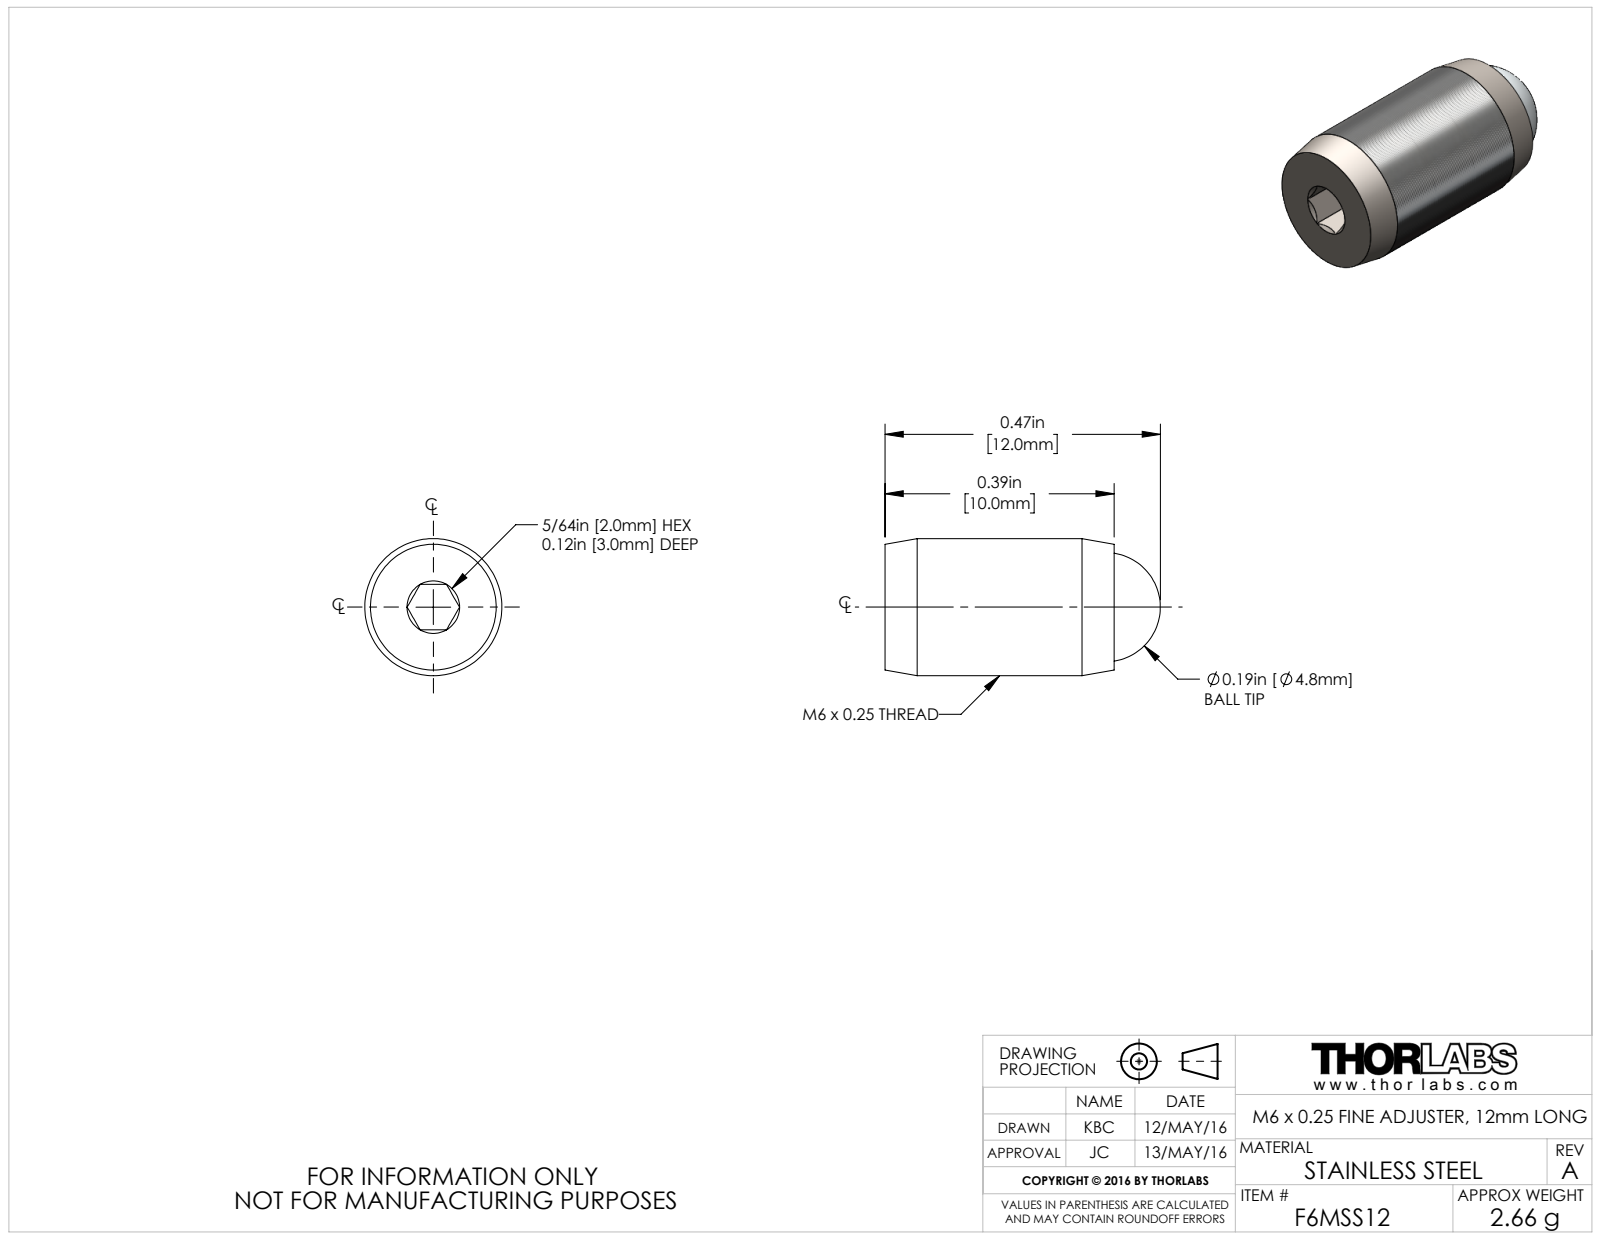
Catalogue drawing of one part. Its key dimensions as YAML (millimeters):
part_name: "TTN102526-E0W"
step_written_by: "SolidWorks 2016 (CONFIG_CONTROL_DESIGN)"
units: millimeters
bodies: {solids: 2, faces: 27, planar: 9, cylindrical: 4, other: 14}
overall_size: [12.02, 5.98, 5.98]
volume: 282
surface_area: 353
round_holes:
  - {diameter: 4.78, count: 1}
round_bosses_or_shafts:
  - {diameter: 5.98, count: 1}
face_to_face_distances: [1.98, 10, 3.05, 6.95]
